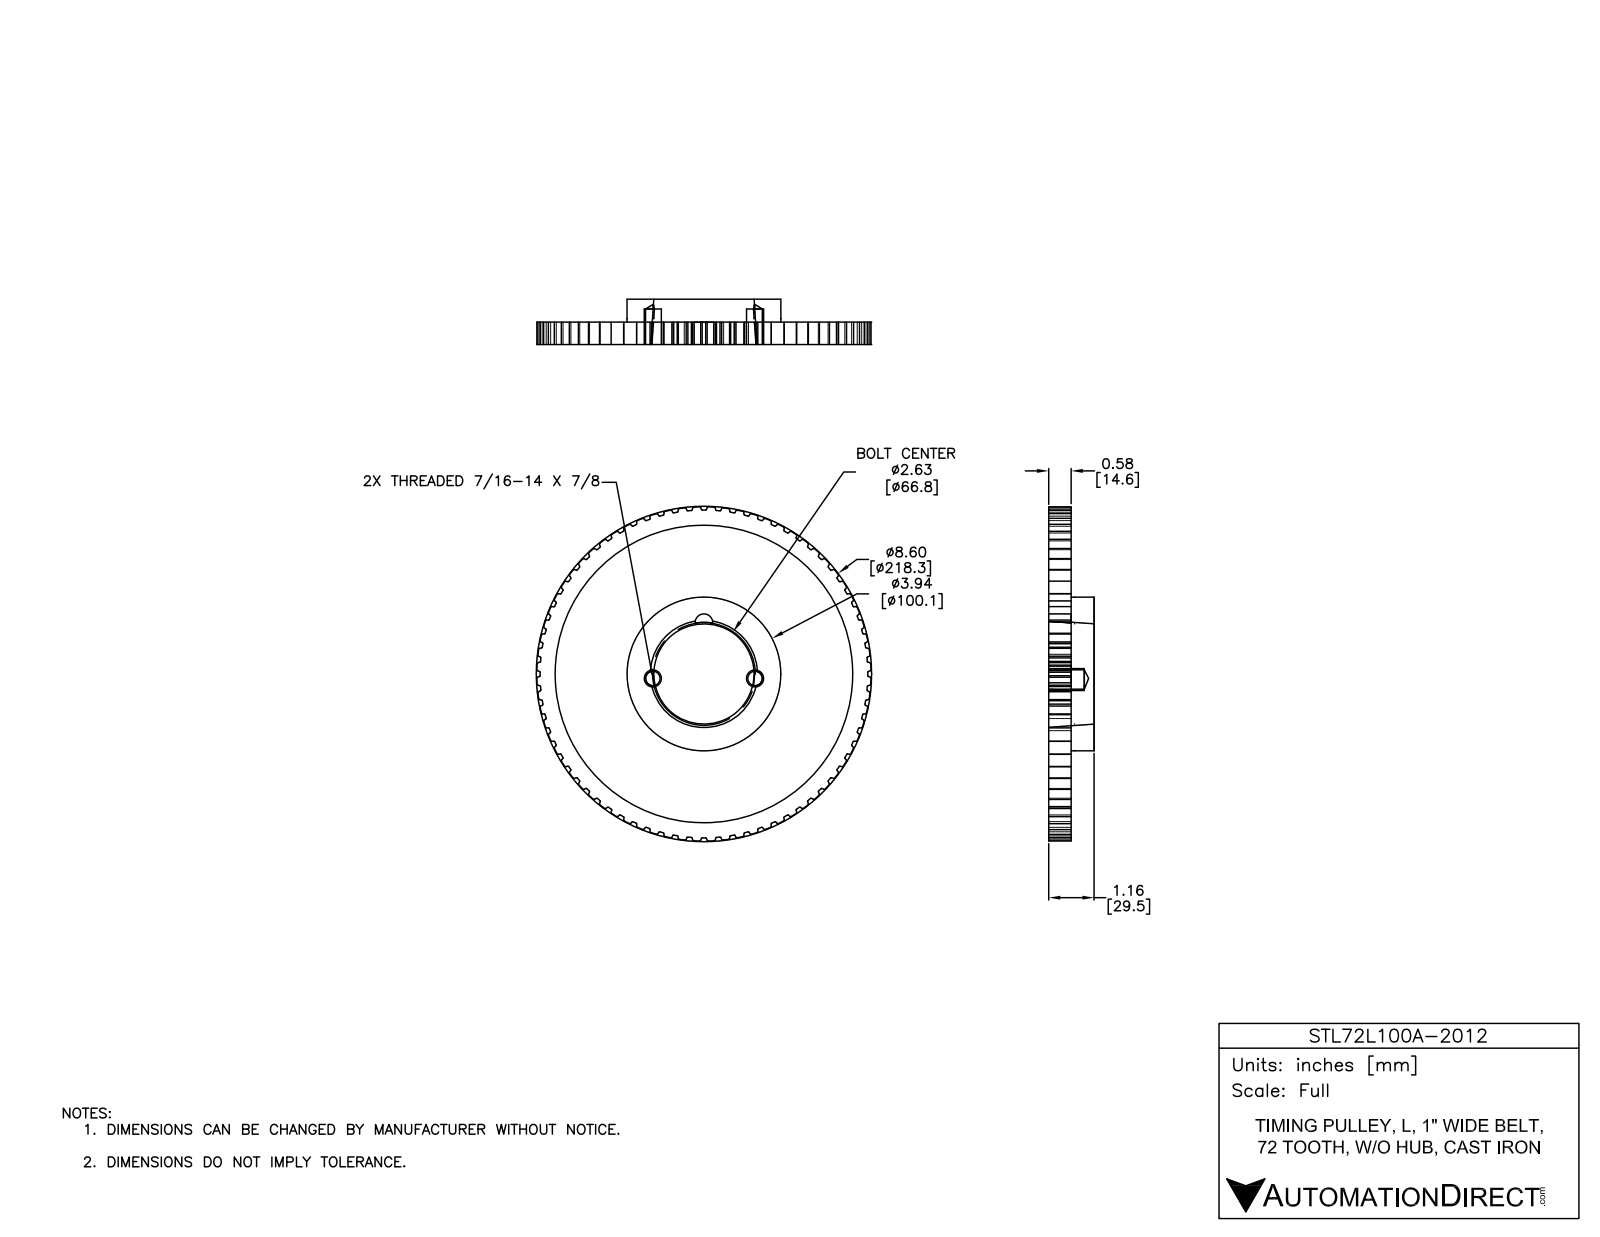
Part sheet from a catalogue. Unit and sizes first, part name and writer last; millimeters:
Units: millimetres
Overall size (bounding box): 217.6 × 217.6 × 27.29
Round holes (diameter × count): ⌀193.7 ×1
Round bosses / shafts (diameter × count): ⌀100.1 ×1
Partial cylindrical surfaces — rounded edges, fillets, slot ends (radius × count): R0.38 ×144, R0.51 ×144, R4.7 ×2, R5.71 ×1, R108.8 ×1
Main face-to-face distances: 12.29, 15, 27.29, 71.63, 71.7, 70.16, 70.13, 70.12, 71.71, 141.86
Volume: 575 370 mm³ · Surface area: 109 610 mm²
Bodies: 1 solid, 655 faces (222 planar, 431 cylindrical, 2 other)
Part name (STEP PRODUCT): STL72L100A-2012
STEP written by: SolidWorks 2018 (AUTOMOTIVE_DESIGN)
